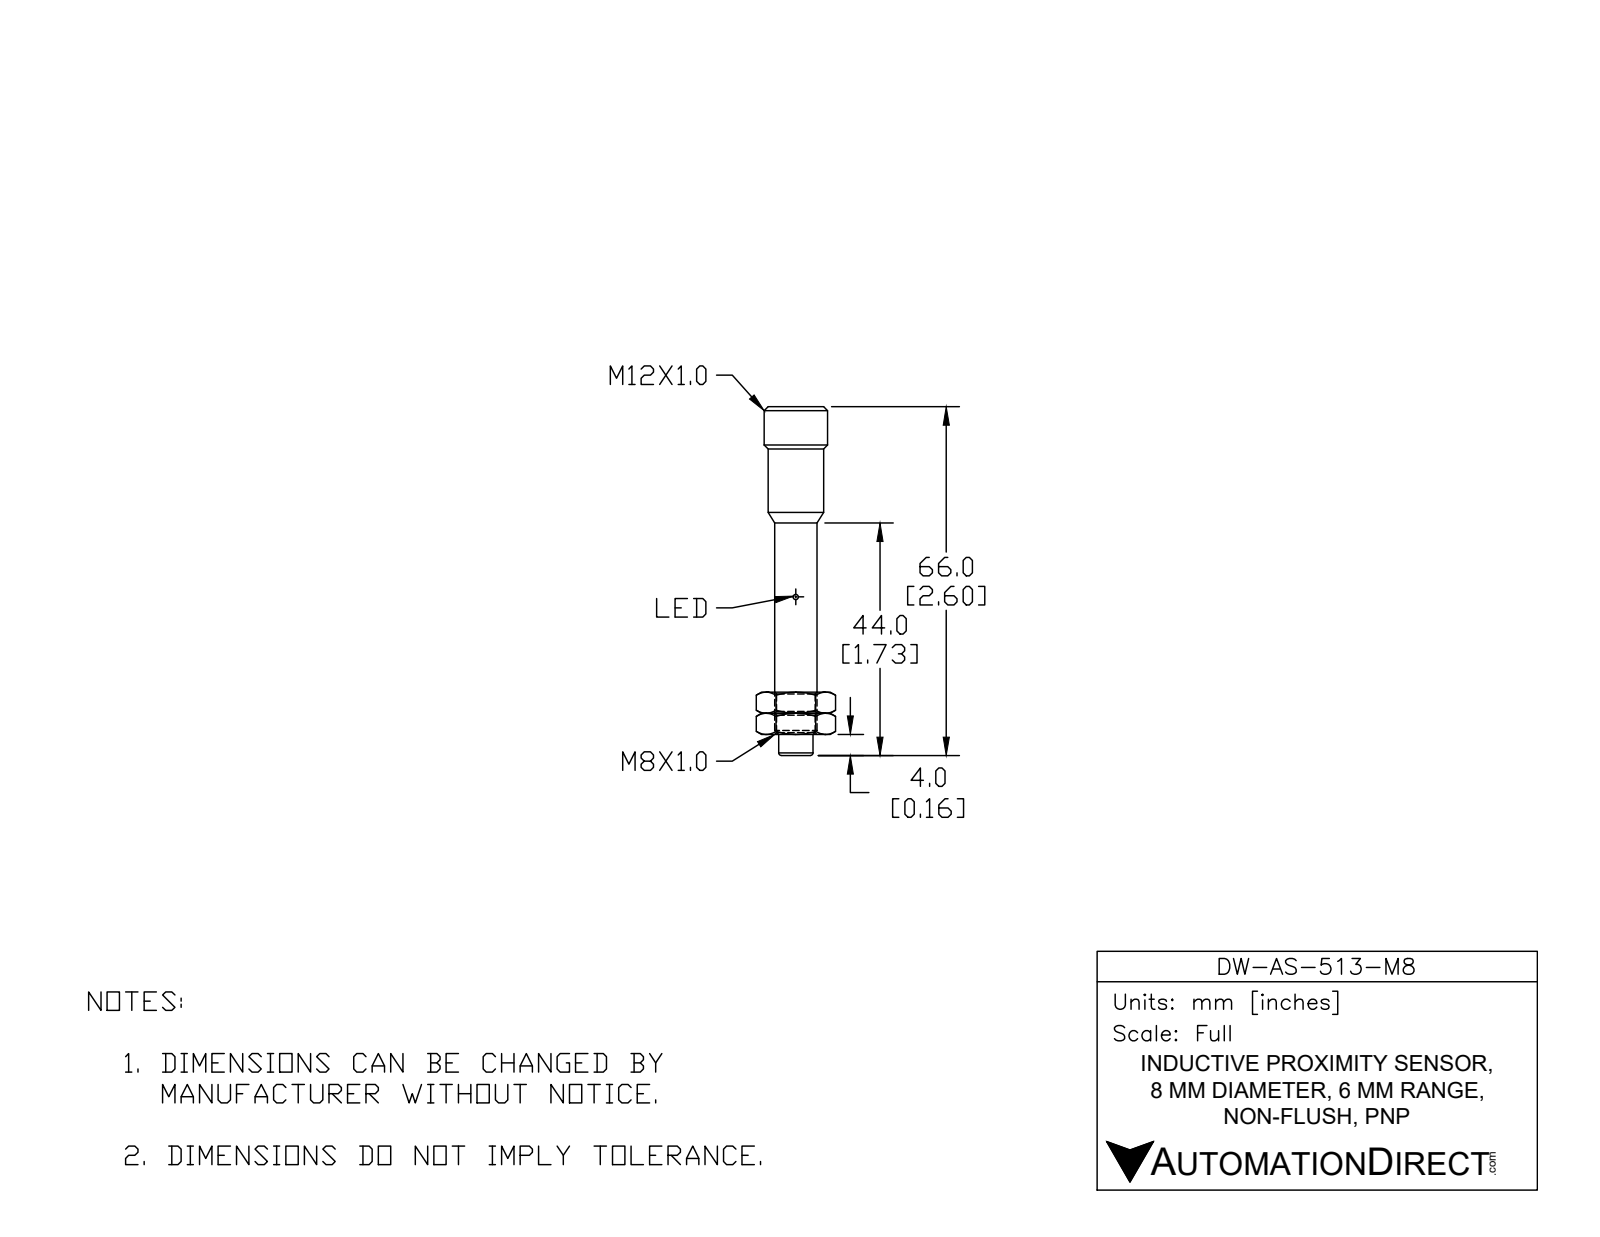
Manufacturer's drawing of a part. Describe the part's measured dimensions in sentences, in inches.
The part is named "DW-AS-513-M8". Its 3-D file was written by "SolidWorks 2017 (AUTOMOTIVE_DESIGN)". It is 1 solid with 35 faces: 10 planar, 17 cylindrical and 8 other. Overall it measures 2.599 by 0.472 by 0.472 inches. Its volume is 0.225 cubic inches and its surface area 3.685 square inches. Round holes: 2 of diameter 0.12. Round bosses or shafts: 4 of diameter 0.039, 1 of diameter 0.472, 1 of diameter 0.415, 1 of diameter 0.335, 1 of diameter 0.315, 1 of diameter 0.272. The main face-to-face distances are 0.343, 2.256, 2.598, 1.811, 0.445, 0.787, 0.165, 1.646, 2.091, 2.433.
